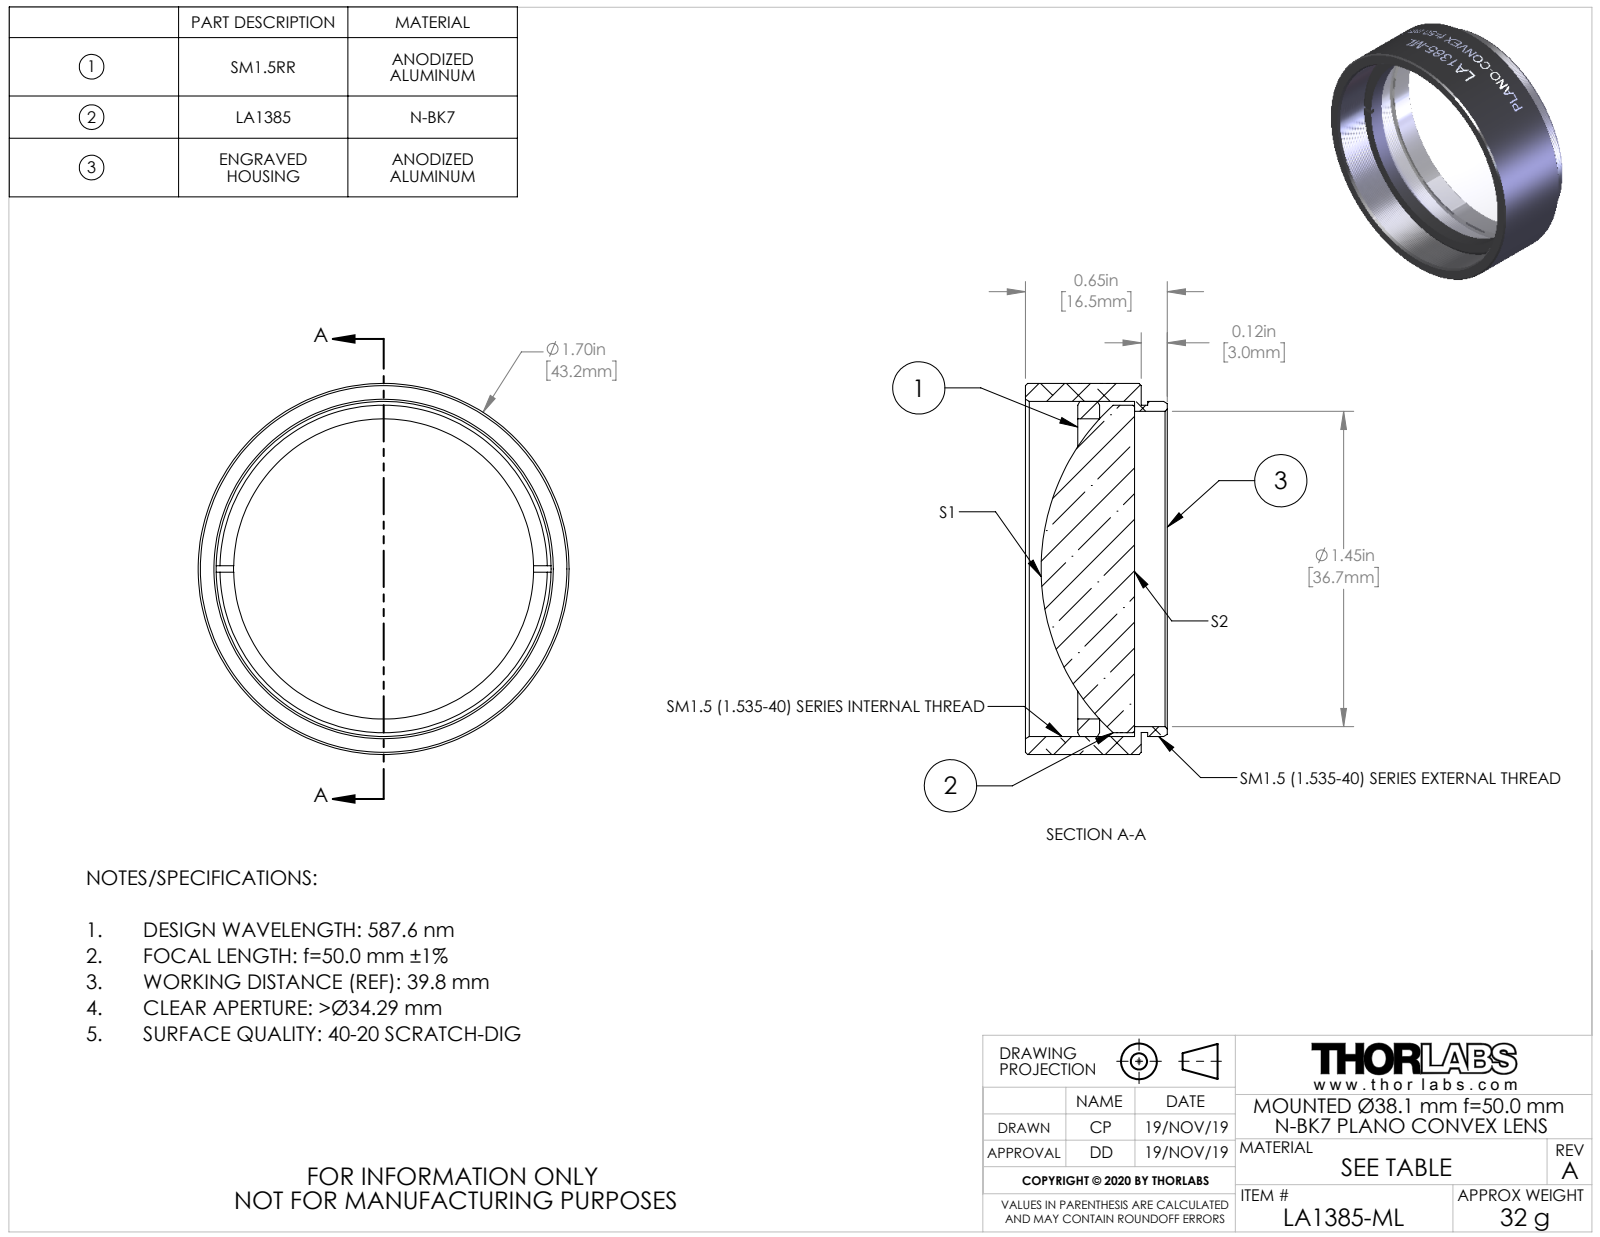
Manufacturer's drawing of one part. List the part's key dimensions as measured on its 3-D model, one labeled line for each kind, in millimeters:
Part name (STEP PRODUCT): TTN200684-E0W
STEP written by: SolidWorks 2018 (CONFIG_CONTROL_DESIGN)
Units: millimetres
Bodies: 3 solids, 118 faces (15 planar, 84 cylindrical, 19 other)
Overall size (bounding box): 43.18 × 43.18 × 16.51
Volume: 12 606 mm³ · Surface area: 8 818 mm²
Round holes (diameter × count): ⌀34.92 ×1, ⌀36.7 ×1
Round bosses / shafts (diameter × count): ⌀43.18 ×1, ⌀38.99 ×1, ⌀38.1 ×1, ⌀38.07 ×1
Main face-to-face distances: 0.76, 13.46, 12.7, 4.85, 4.09, 8.61, 7.39, 6.63, 2.54, 6.07
